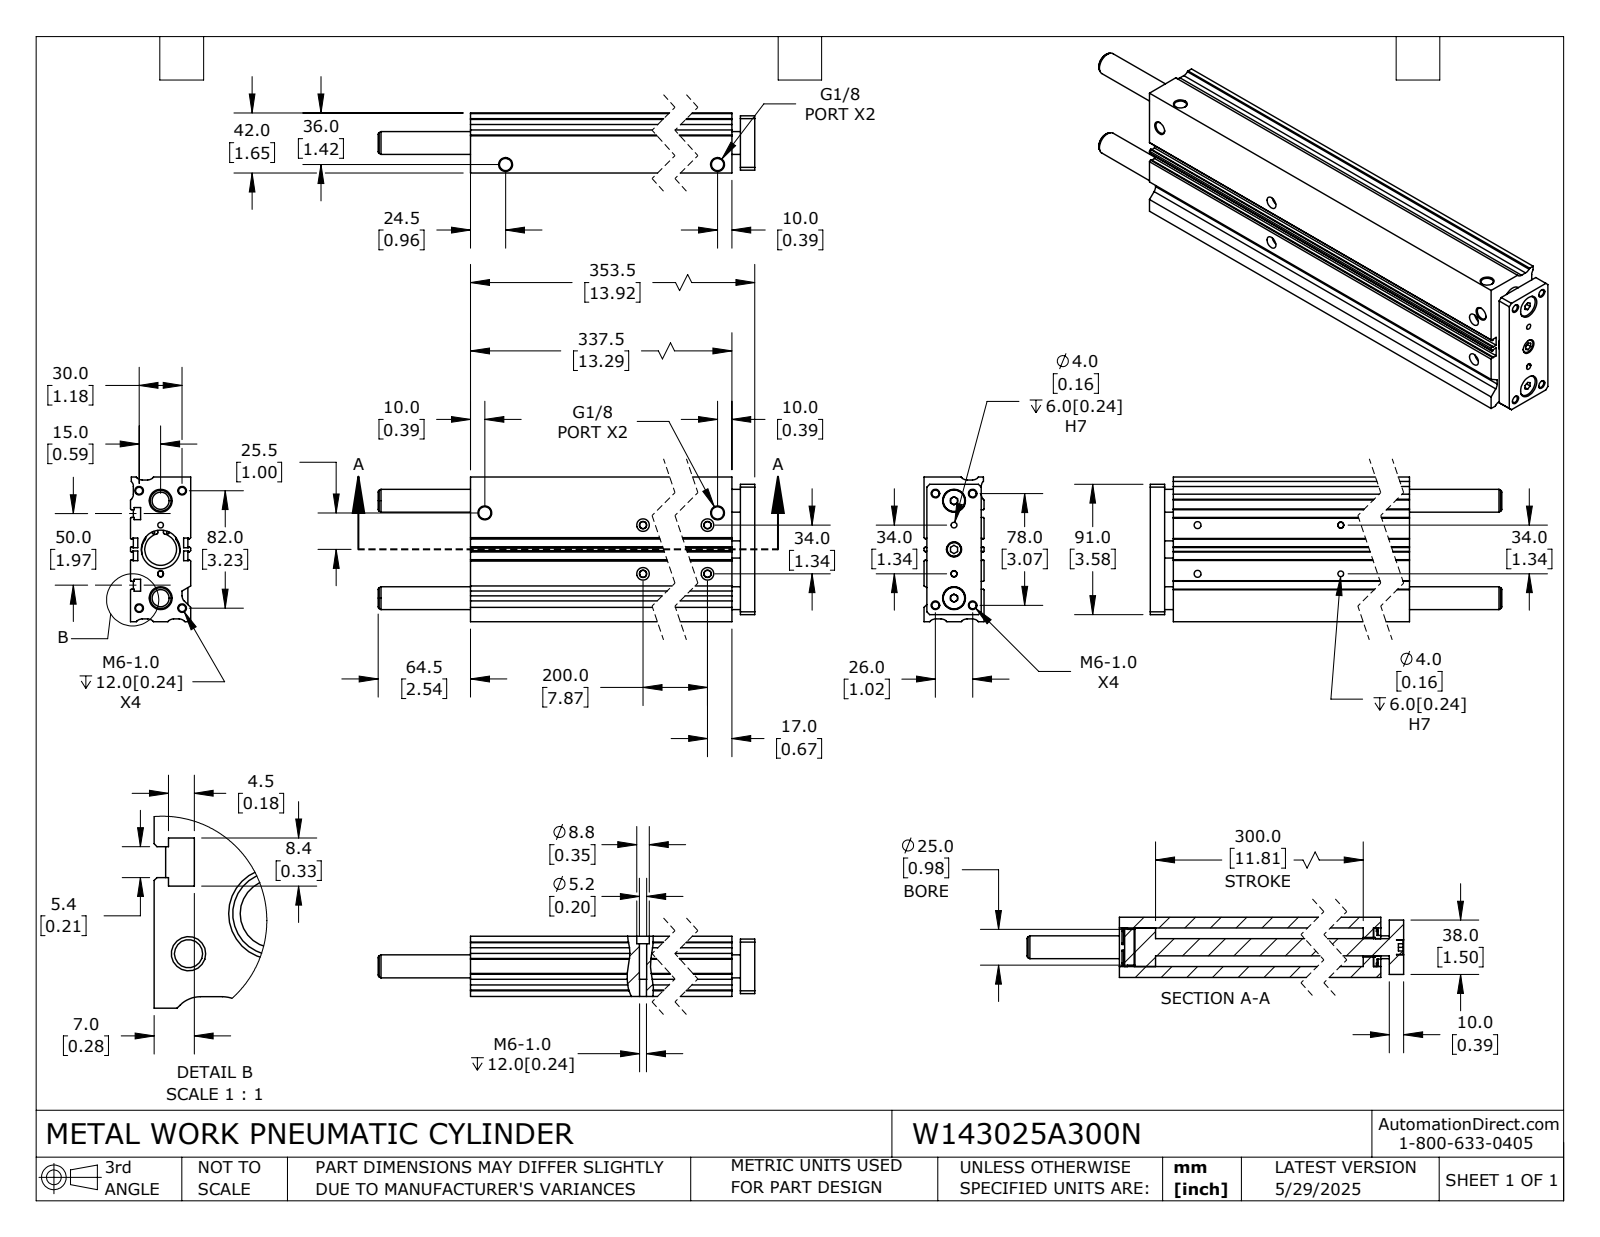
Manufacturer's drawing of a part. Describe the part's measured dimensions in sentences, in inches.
The part is named "W143025A300N; W143025A300N_ROD; W143025A300N_BODY". Its 3-D file was written by "SolidWorks 2024 (CONFIG_CONTROL_DESIGN)". It is 6 solids with 390 faces: 191 planar, 157 cylindrical and 42 other. Overall it measures 16.457 by 3.976 by 1.654 inches. Its volume is 74.41 cubic inches and its surface area 424 square inches. Round holes: 8 of diameter 0.194, 4 of diameter 0.067, 4 of diameter 0.157, 4 of diameter 0.194, 4 of diameter 0.205, 4 of diameter 0.337, 4 of diameter 0.346, 2 of diameter 0.63, 1 of diameter 0.413, 1 of diameter 0.472, 1 of diameter 0.539, 1 of diameter 0.874. Round bosses or shafts: 2 of diameter 0.61, 1 of diameter 1.063, 1 of diameter 0.984, 1 of diameter 0.65, 1 of diameter 0.394. Partial cylindrical surfaces (rounded edges, fillets, slot ends): 12 of radius 0.039, 9 of radius 0.197, 8 of radius 0.079, 2 of radius 0.524, 1 of radius 0.559. The main face-to-face distances are 1.654, 0.079, 0.197, 1.378, 1.457, 0.839, 3.976, 2.299, 0.276, 0.354. The hole center spacings are 1.339, 0.111, 0.29, 0.5, 0.548, 0.652, 0.669, 0.902.
